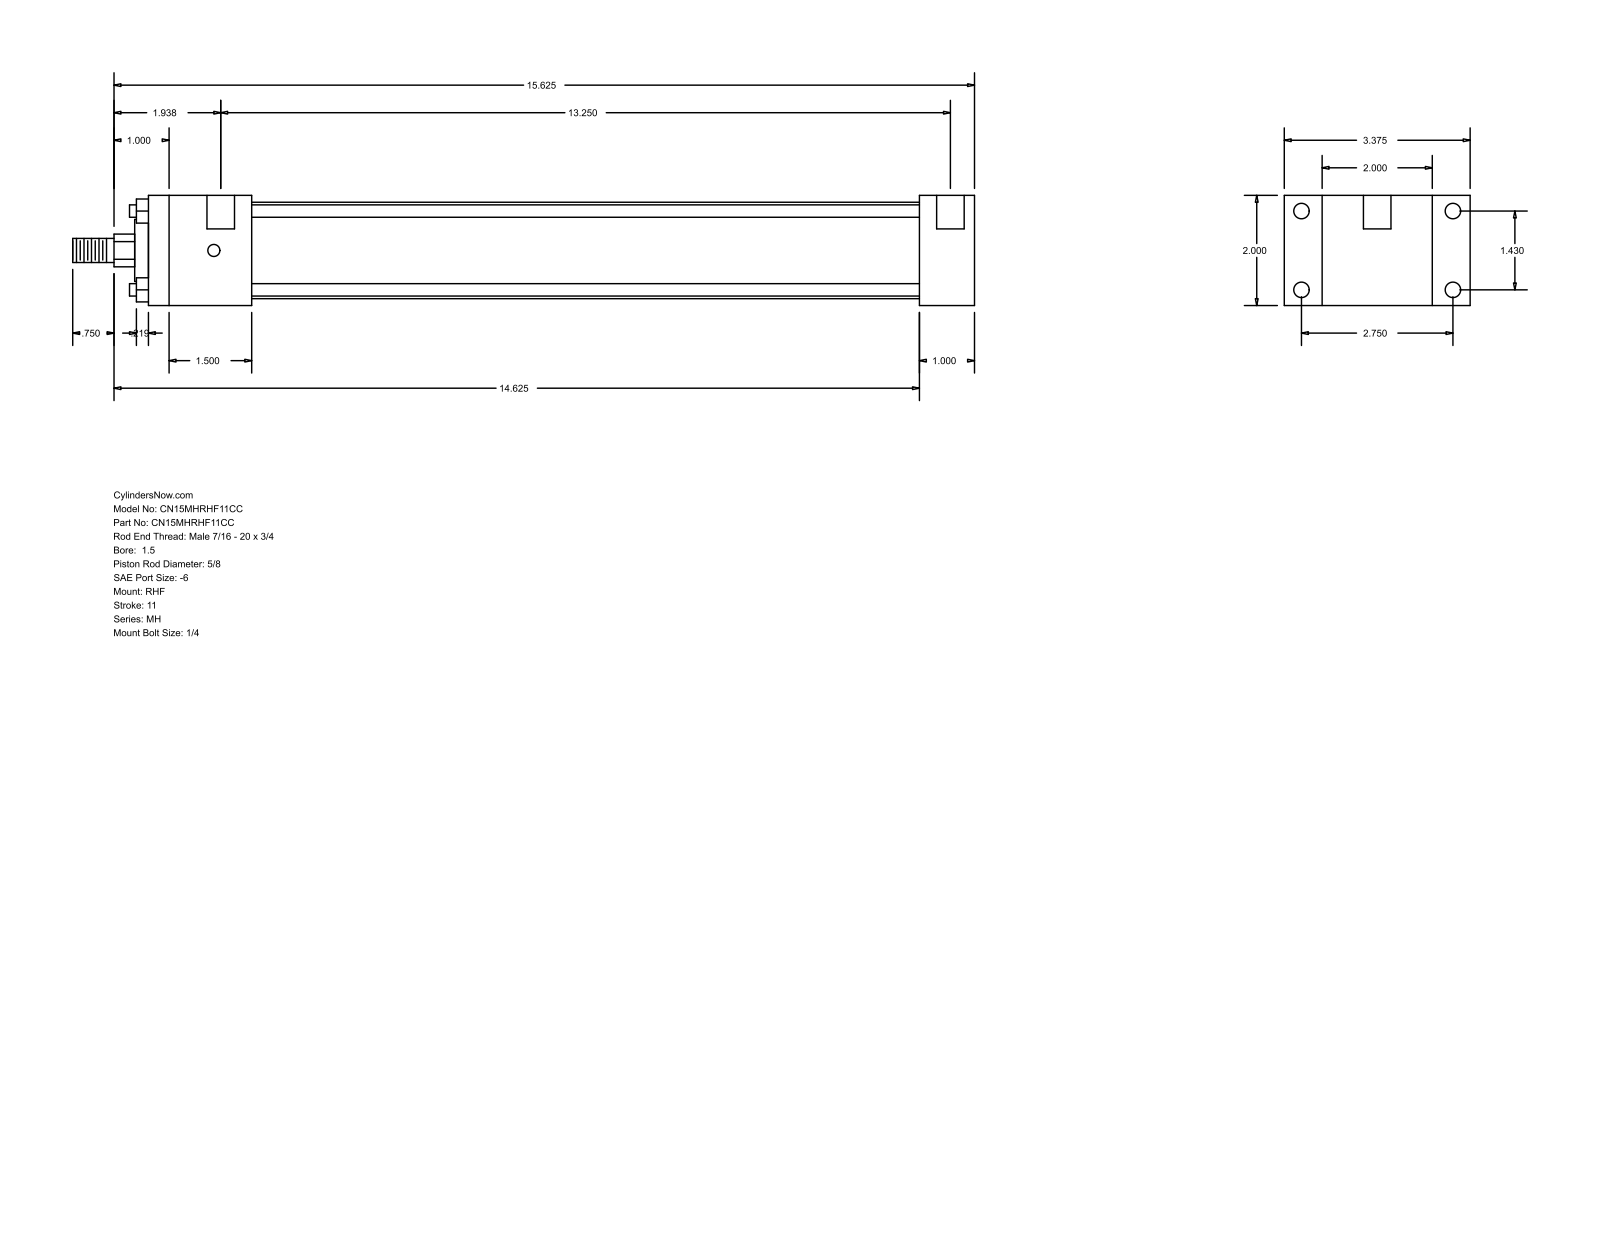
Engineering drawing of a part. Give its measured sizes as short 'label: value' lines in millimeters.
name: MH_RHF__0150_0.625
written by: GSSL Pune (CONFIG_CONTROL_DESIGN)
unit: mm
bodies: 0 solids, 88 faces (60 planar, 28 cylindrical, 0 other)
size: 415.93 × 85.72 × 50.8
holes: 4× ⌀5.56, 4× ⌀7.14, 2× ⌀12.7
bosses: 4× ⌀5.71, 1× ⌀44.45, 1× ⌀28.57, 1× ⌀15.88, 1× ⌀11.11
rounds: 1× R7.54
face distances: 50.8, 25.4, 17.46, 68.26, 355.6, 381, 85.72, 47.62, 307.98, 333.38
hole spacings: 36.32, 69.84, 78.72, 339.72, 3.17, 336.55
